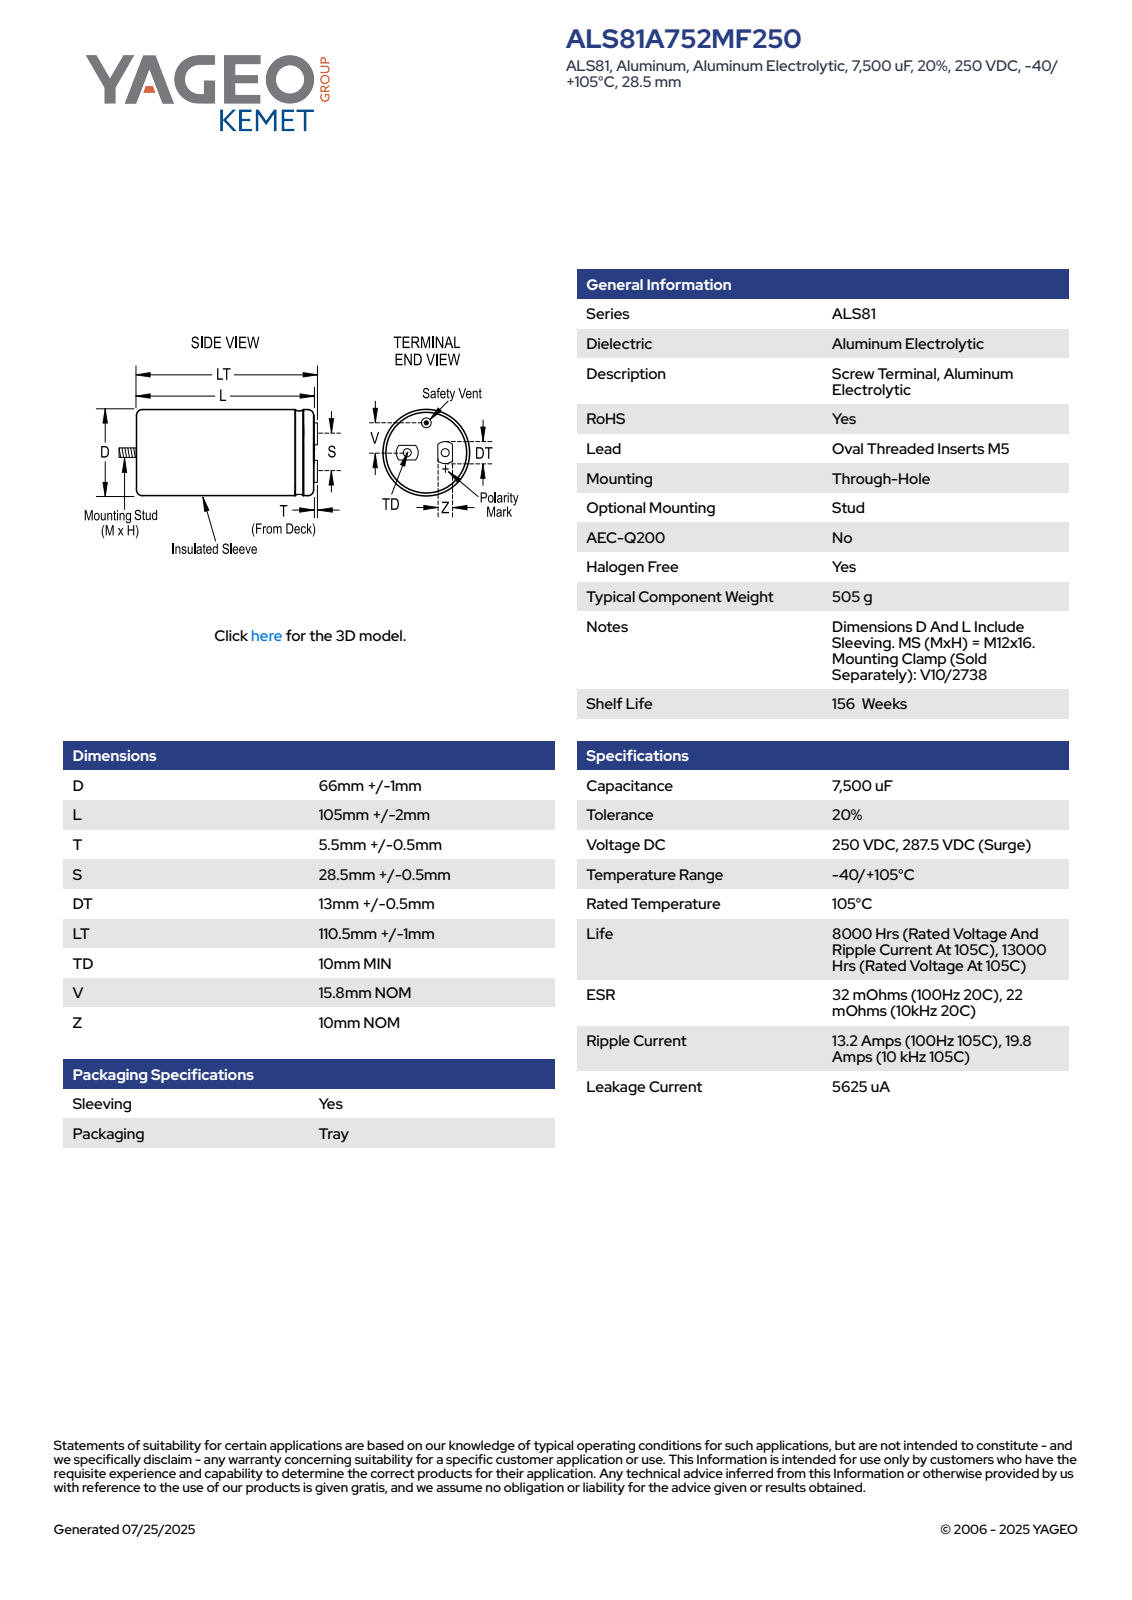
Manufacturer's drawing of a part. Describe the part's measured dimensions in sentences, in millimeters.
The part is named "CARC_KALSOS_66X105_D67L107T6S28.5DT13.5TD10.000LT111.500V15.800". Its 3-D file was written by "SolidWorks 2014 (AUTOMOTIVE_DESIGN)". It is 1 solid with 98 faces: 35 planar, 24 cylindrical and 39 other. Overall it measures 127.5 by 67 by 67 millimeters. Its volume is 375 260 cubic millimeters and its surface area 31 222 square millimeters. Round holes: 2 of diameter 5, 1 of diameter 2, 1 of diameter 63. Round bosses or shafts: 1 of diameter 67, 1 of diameter 12, 1 of diameter 3. Partial cylindrical surfaces (rounded edges, fillets, slot ends): 4 of radius 8, 1 of radius 33.49. The main face-to-face distances are 106, 111.5, 5.5, 10, 16, 122, 127.5, 117.5, 101.5, 4.5. The hole center spacings are 14.25, 21.28, 15.8, 28.5.
